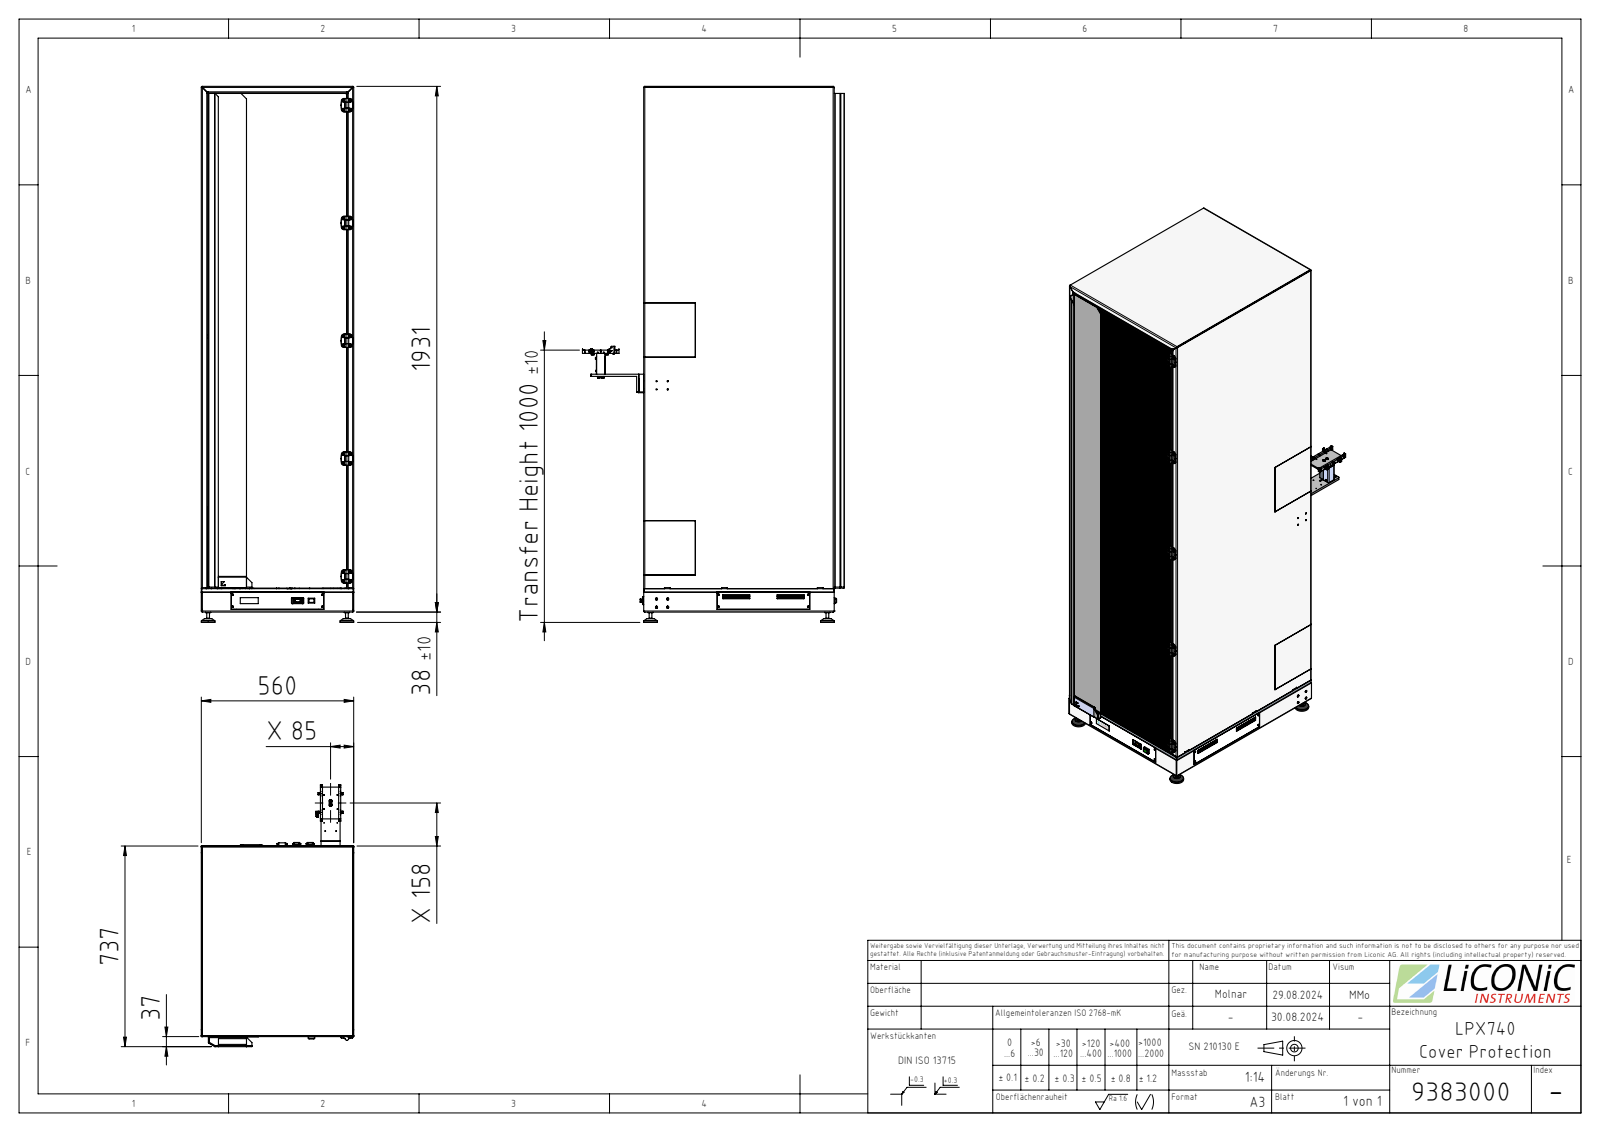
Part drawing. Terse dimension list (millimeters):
name: 9383000
written by: SolidWorks 2022 (AUTOMOTIVE_DESIGN)
unit: mm
bodies: 83 solids, 10107 faces (5239 planar, 4660 cylindrical, 208 other)
size: 1969 × 962.18 × 560.01
volume: 27 550 000 mm³; area: 16 290 000 mm²
holes: 178× ⌀4, 82× ⌀2.5, 71× ⌀4.2, 57× ⌀3.3, 32× ⌀6.5, 30× ⌀4.4, 27× ⌀4.5, 20× ⌀3, 20× ⌀9, 16× ⌀3.4, 16× ⌀7.1, 14× ⌀6
bosses: 5× ⌀22, 4× ⌀50.01, 4× ⌀10, 3× ⌀1.5, 1× ⌀540, 1× ⌀234, 1× ⌀15.5, 1× ⌀14.5
rounds: 832× R0.1, 832× R0.25, 717× R2, 160× R1, 121× R5, 114× R2.5, 68× R3, 40× R1.7
face distances: 2, 558, 560, 556, 700, 698, 5, 693, 695, 1929
hole spacings: 23, 46, 69, 92, 115, 138, 161, 184
